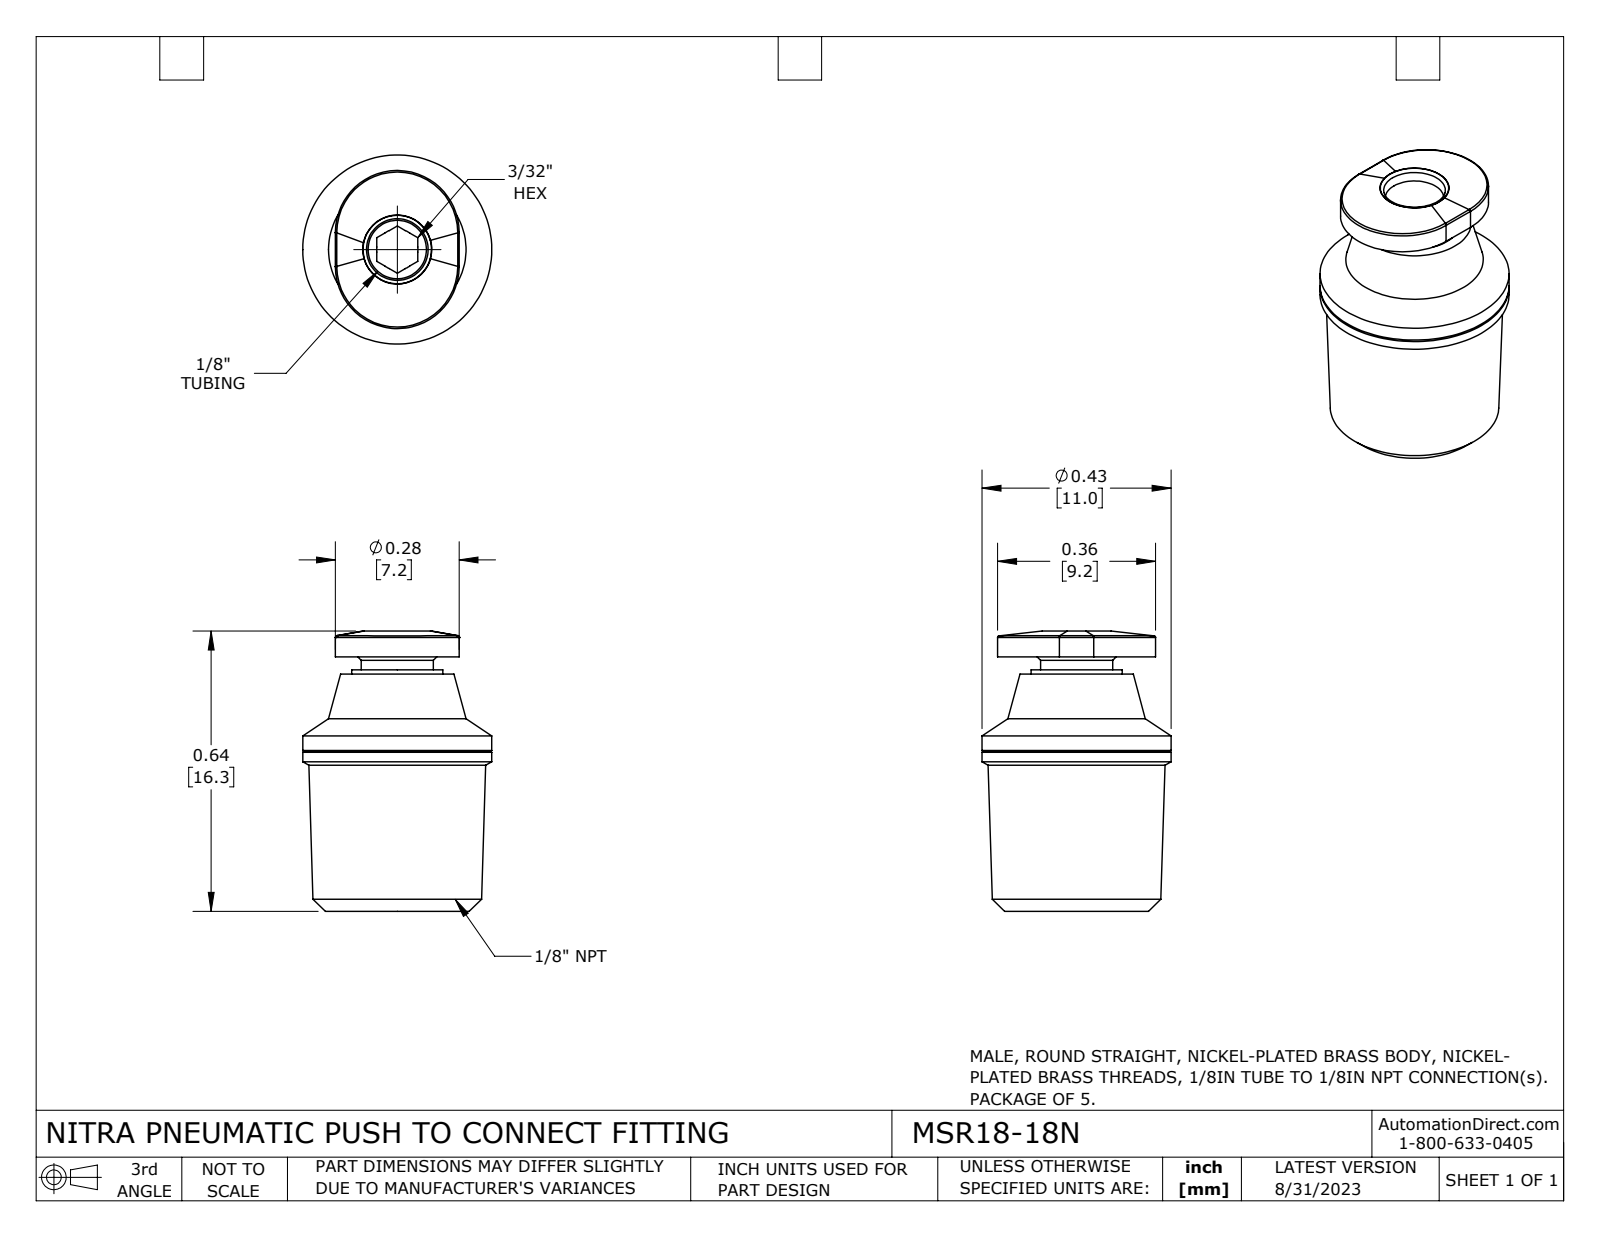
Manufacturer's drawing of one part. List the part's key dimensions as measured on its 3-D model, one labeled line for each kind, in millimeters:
Part name (STEP PRODUCT): MSR18-18N
STEP written by: SolidWorks 2015 (CONFIG_CONTROL_DESIGN)
Units: millimetres
Bodies: 1 solid, 55 faces (8 planar, 15 cylindrical, 32 other)
Overall size (bounding box): 16.3 × 11 × 11
Volume: 970 mm³ · Surface area: 830 mm²
Round holes (diameter × count): ⌀2.4 ×1, ⌀3.4 ×1
Round bosses / shafts (diameter × count): ⌀11 ×1, ⌀5.3 ×1, ⌀4.2 ×1
Partial cylindrical surfaces — rounded edges, fillets, slot ends (radius × count): R3.6 ×2
Main face-to-face distances: 14.8, 13.8, 1, 14, 0.8, 5, 8.8, 9, 9.8, 7.2
